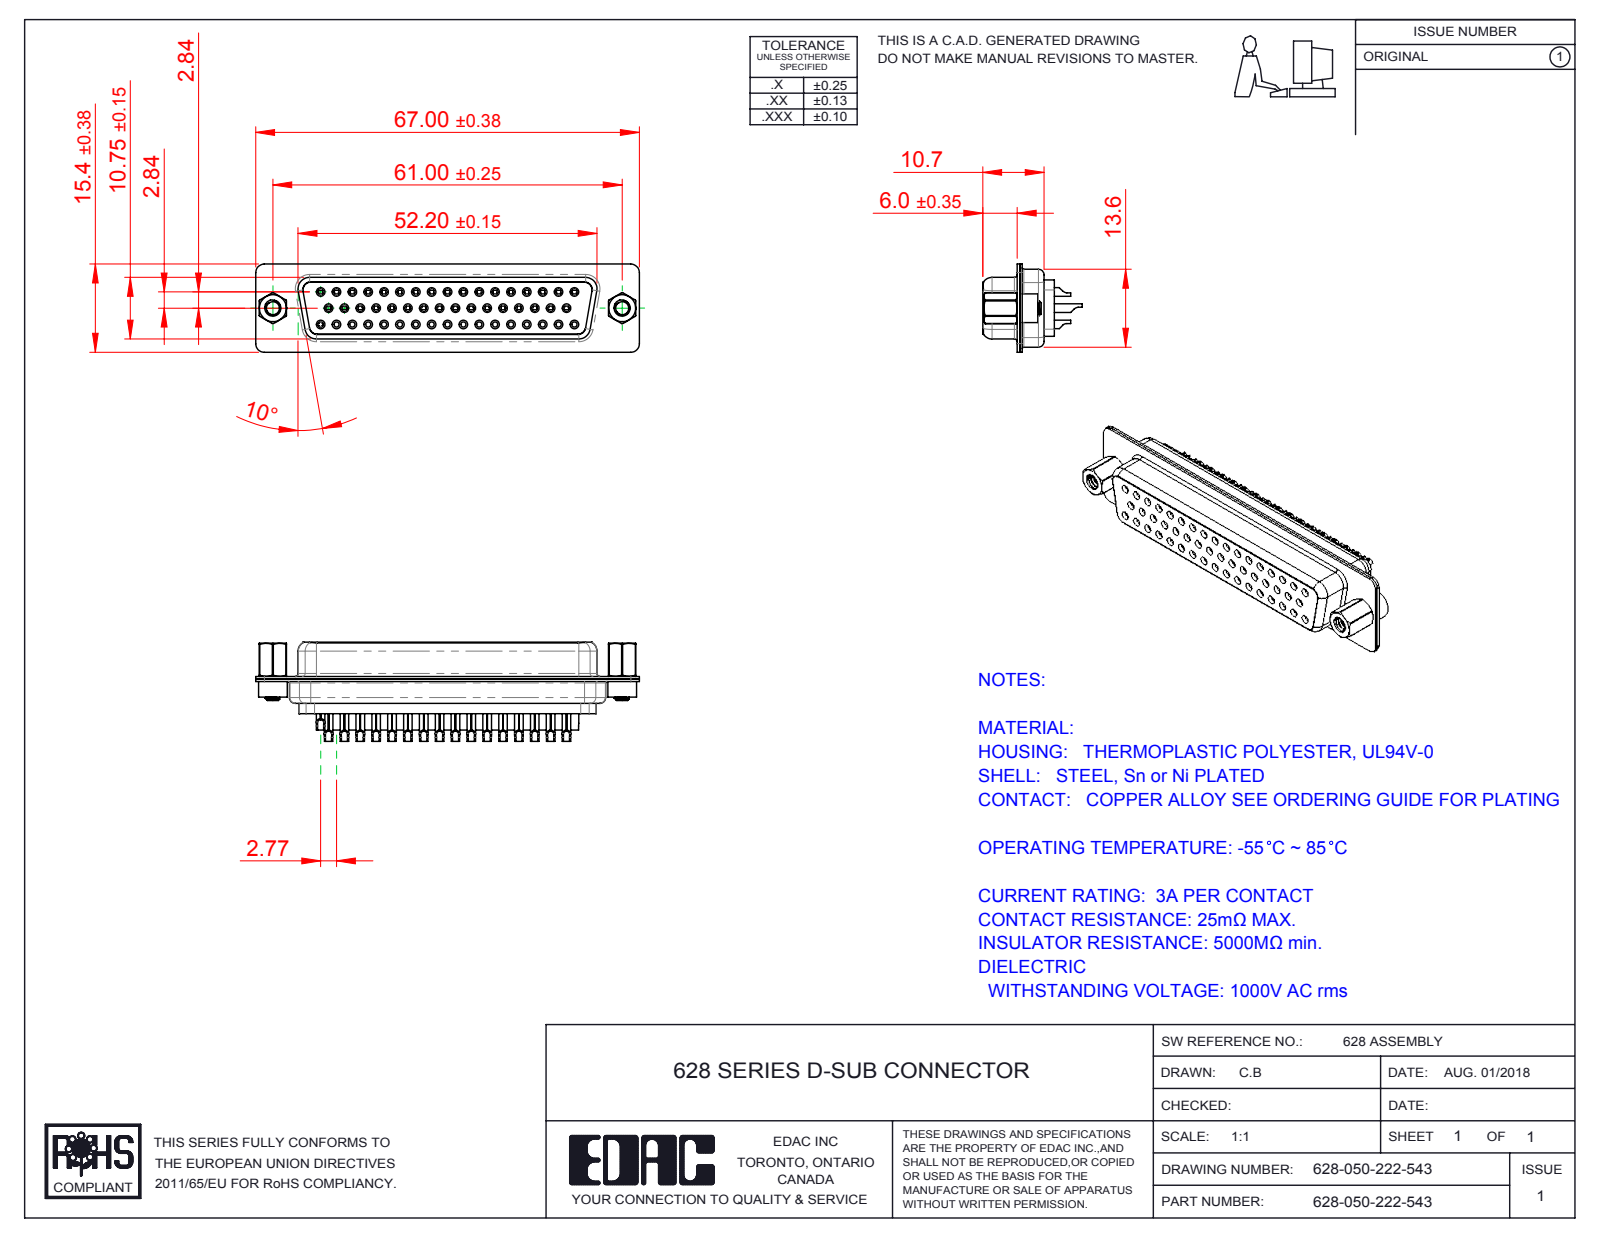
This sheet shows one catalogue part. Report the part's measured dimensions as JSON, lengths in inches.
{"part_name": "628 Contact Row 2_22M; 628 Shell Rear_50 Contacts; 628-050-222-543; 628 Housing_50 LP (+5 more)", "step_written_by": "SolidWorks 2016 (CONFIG_CONTROL_DESIGN)", "units": "inches", "bodies": {"solids": 41, "faces": 3639, "planar": 851, "cylindrical": 1187, "other": 1601}, "overall_size": [2.638, 0.683, 0.606], "volume_in3": 0.418, "surface_area_in2": 22.65, "round_holes": [[0.035, 50], [0.063, 50], [0.031, 34], [0.043, 34], [0.067, 17], [0.059, 16], [0.079, 16], [0.089, 2], [0.09, 2], [0.157, 2], [0.189, 2]], "round_bosses_or_shafts": [[0.079, 34], [0.059, 34], [0.047, 34], [0.197, 2], [0.193, 2], [0.11, 2]], "partial_cylinders_radius": [[0.011, 33], [0.059, 16], [0.079, 12], [0.053, 8], [0.039, 7], [0.01, 4], [0.02, 4], [0.024, 4]], "face_to_face_distances": [0.018, 0.016, 0.406, 0.035, 0.238, 0.256, 0.492, 0.254, 0.236, 0.446], "hole_center_spacings": [0.124, 0.109, 0.218, 0.327, 0.436, 0.545, 0.654, 0.763]}
